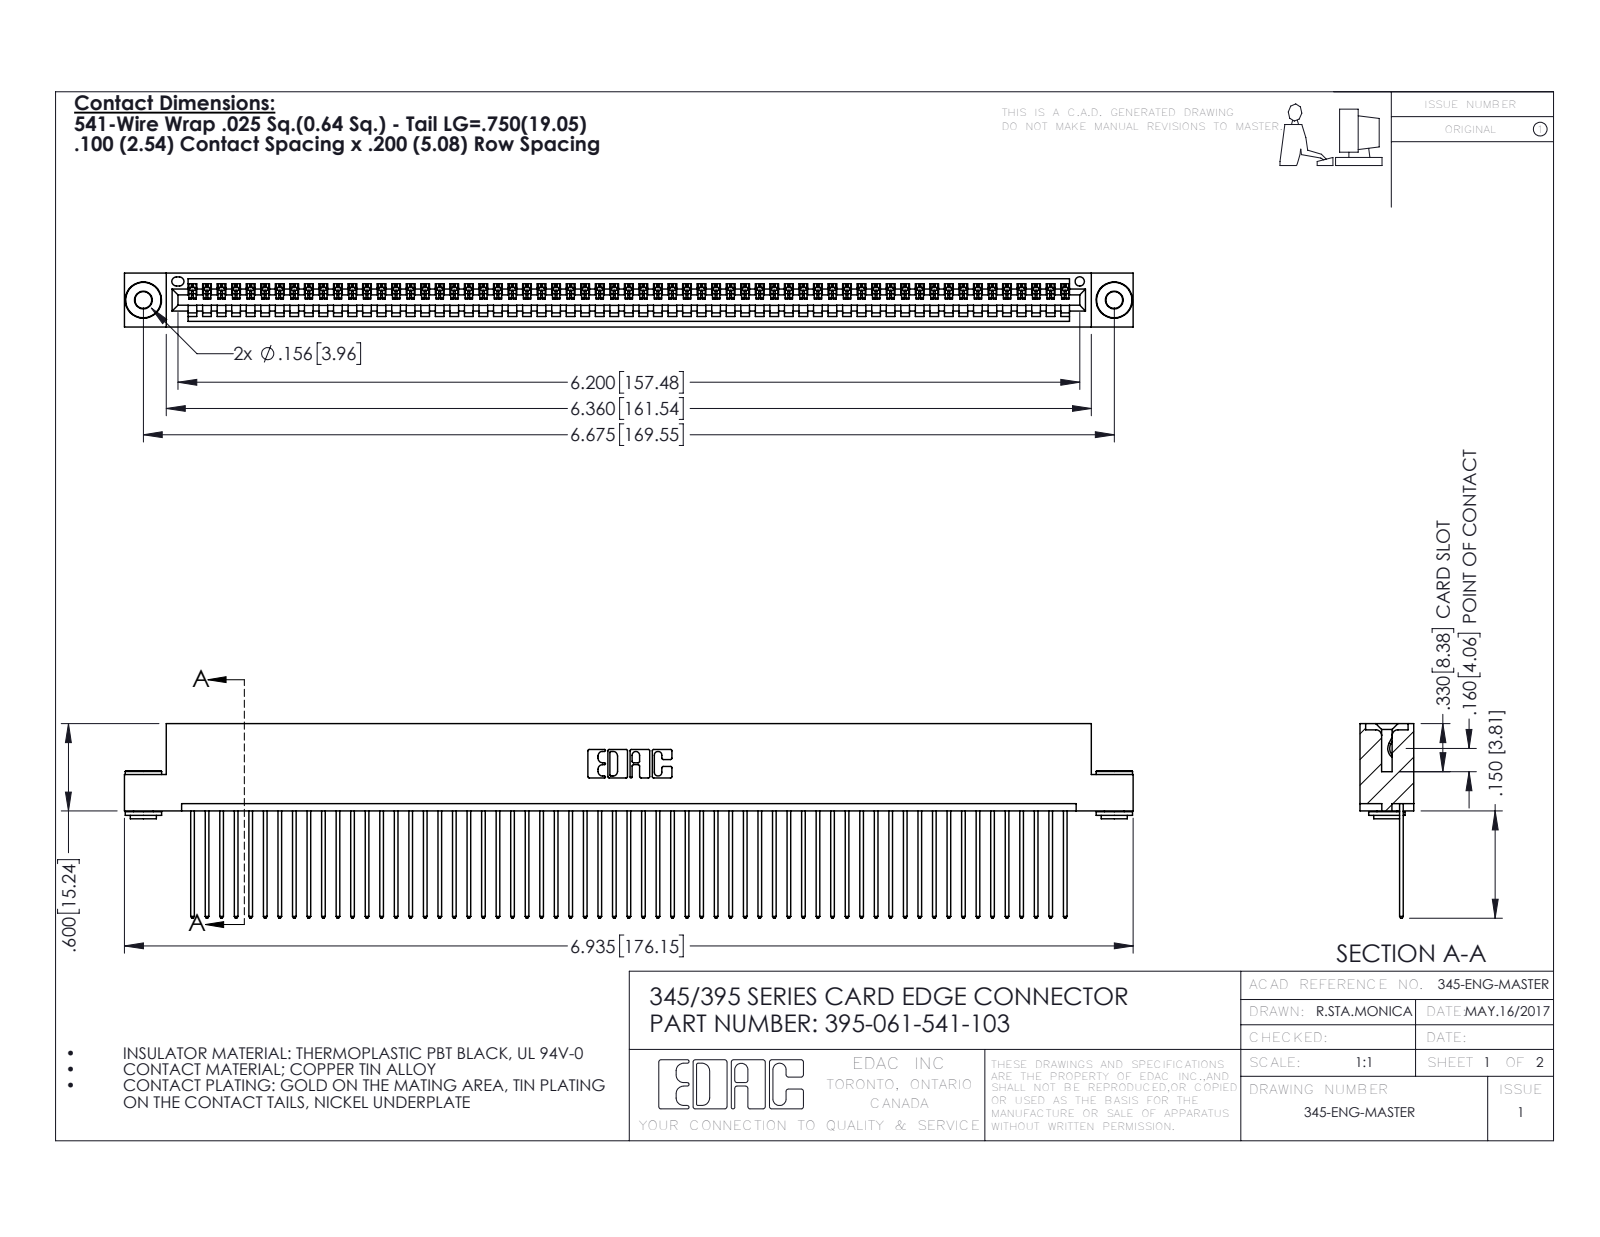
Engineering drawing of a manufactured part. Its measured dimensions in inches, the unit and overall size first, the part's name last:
Units: inches
Overall size (bounding box): 6.935 × 1.337 × 0.37
Round holes (diameter × count): ⌀0.116 ×2, ⌀0.156 ×2, ⌀0.064 ×1
Round bosses / shafts (diameter × count): ⌀0.25 ×2, ⌀0.18 ×2, ⌀0.136 ×2
Partial cylindrical surfaces — rounded edges, fillets, slot ends (radius × count): R0.006 ×122, R0.01 ×122, R0.01 ×22, R0.007 ×6, R0.031 ×6, R0.026 ×3, R0.031 ×2, R0.04 ×2
Main face-to-face distances: 0.072, 0.298, 0.025, 0.098, 0.272, 0.37, 0.2, 0.225, 0.149, 0.072
Hole centre spacings: 0.27, 6.439, 6.675
Volume: 1.044 in³ · Surface area: 37.81 in²
Bodies: 64 solids, 3702 faces (2530 planar, 1164 cylindrical, 8 other)
Part name (STEP PRODUCT): 345 Part_Flush Mounting Lugs - 0.156 Dia-TH; 345-292-001_345-293-141; 345-250-002_345-250-002-102; 395-061-541-103
STEP written by: SolidWorks 2016 (CONFIG_CONTROL_DESIGN)
